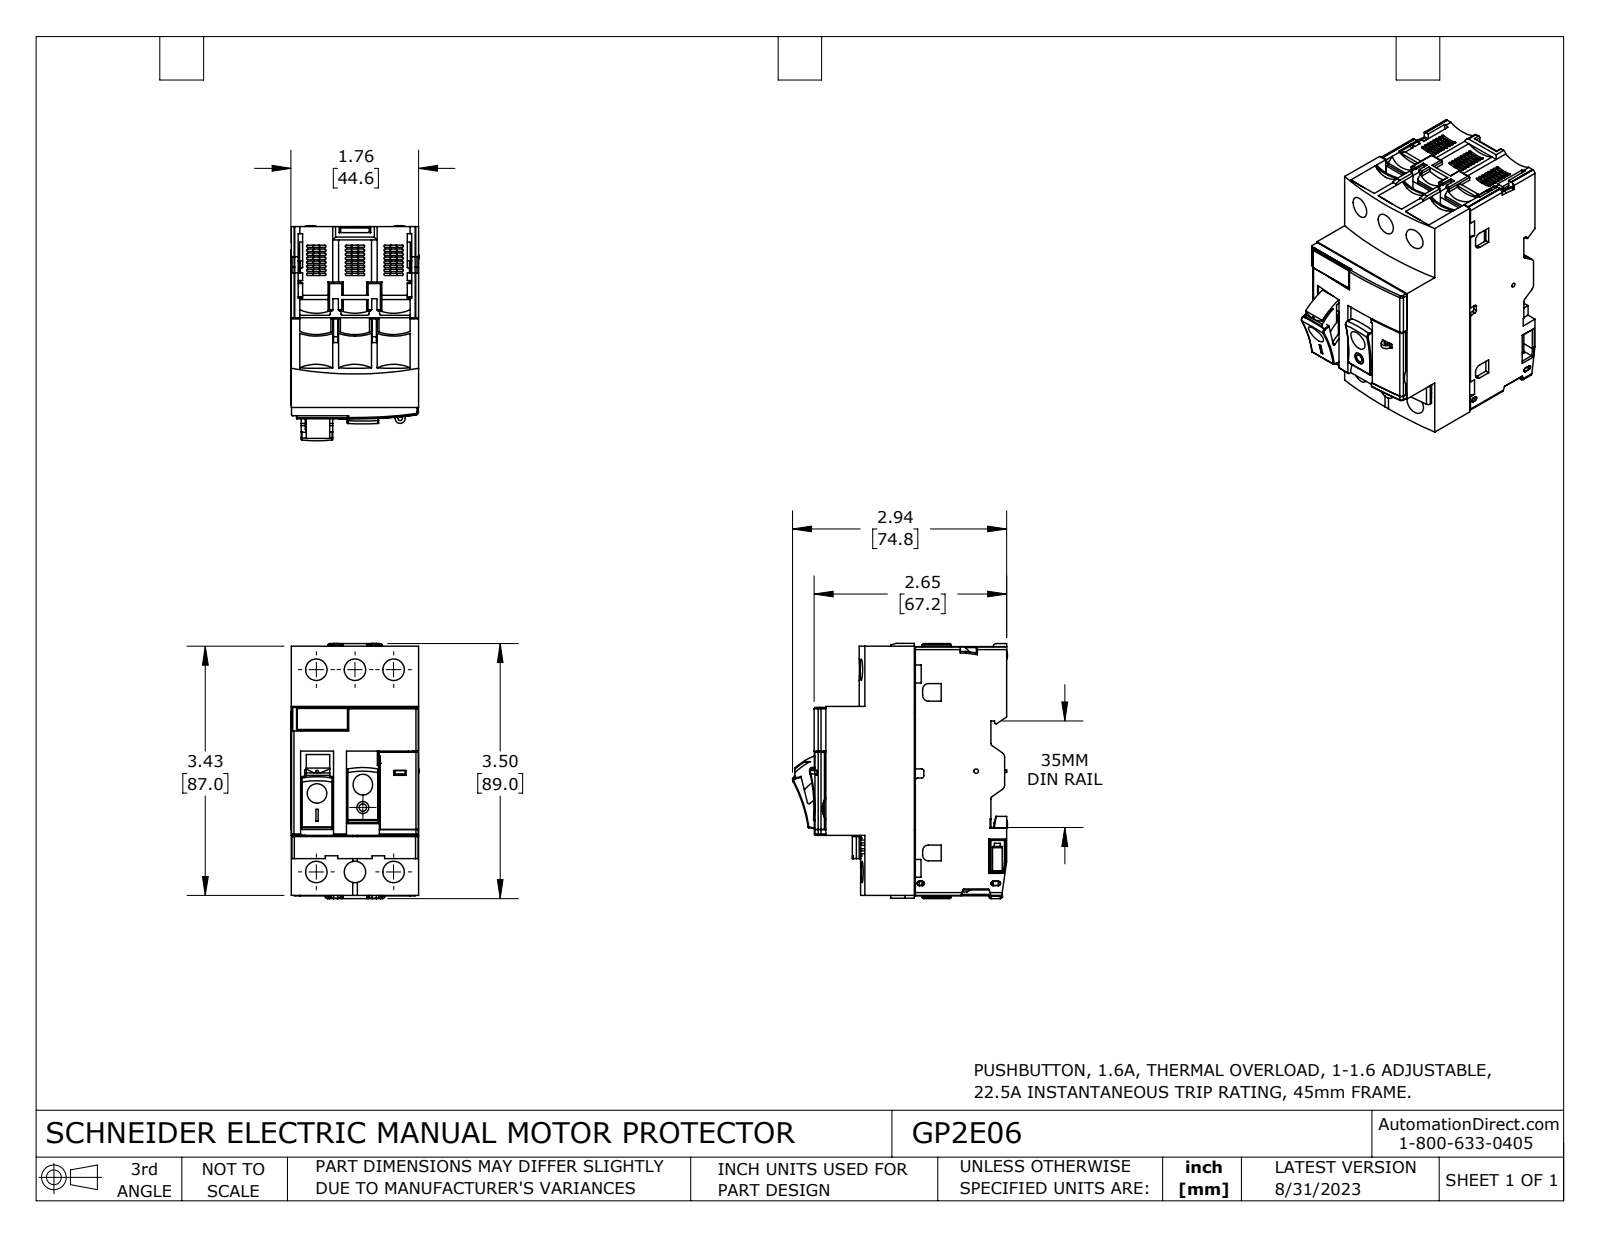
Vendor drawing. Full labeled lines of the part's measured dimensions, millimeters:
Part name (STEP PRODUCT): GP2E06
STEP written by: SolidWorks 2021 (CONFIG_CONTROL_DESIGN)
Units: millimetres
Bodies: 15 solids, 2269 faces (1521 planar, 657 cylindrical, 91 other)
Overall size (bounding box): 89.1 × 75.1 × 44.8
Volume: 189 800 mm³ · Surface area: 63 830 mm²
Round holes (diameter × count): ⌀7.5 ×6, ⌀5 ×5, ⌀1.5 ×2, ⌀4 ×1, ⌀4.2 ×1, ⌀8 ×1, ⌀8.3 ×1, ⌀8.5 ×1, ⌀8.7 ×1
Round bosses / shafts (diameter × count): ⌀6.2 ×2, ⌀3 ×2, ⌀9.7 ×1, ⌀2.6 ×1, ⌀1.2 ×1
Partial cylindrical surfaces — rounded edges, fillets, slot ends (radius × count): R0.4 ×104, R0.5 ×47, R1 ×16, R0.3 ×12, R0.3 ×12, R0.8 ×12, R1.5 ×8, R0.1 ×6
Main face-to-face distances: 44.5, 13.5, 2.9, 31.3, 44.6, 1.5, 41.6, 14.8, 26.7, 29.7
Hole centre spacings: 13.5, 71.9, 70.6, 8.8, 10.2, 13.9, 17, 18.4
